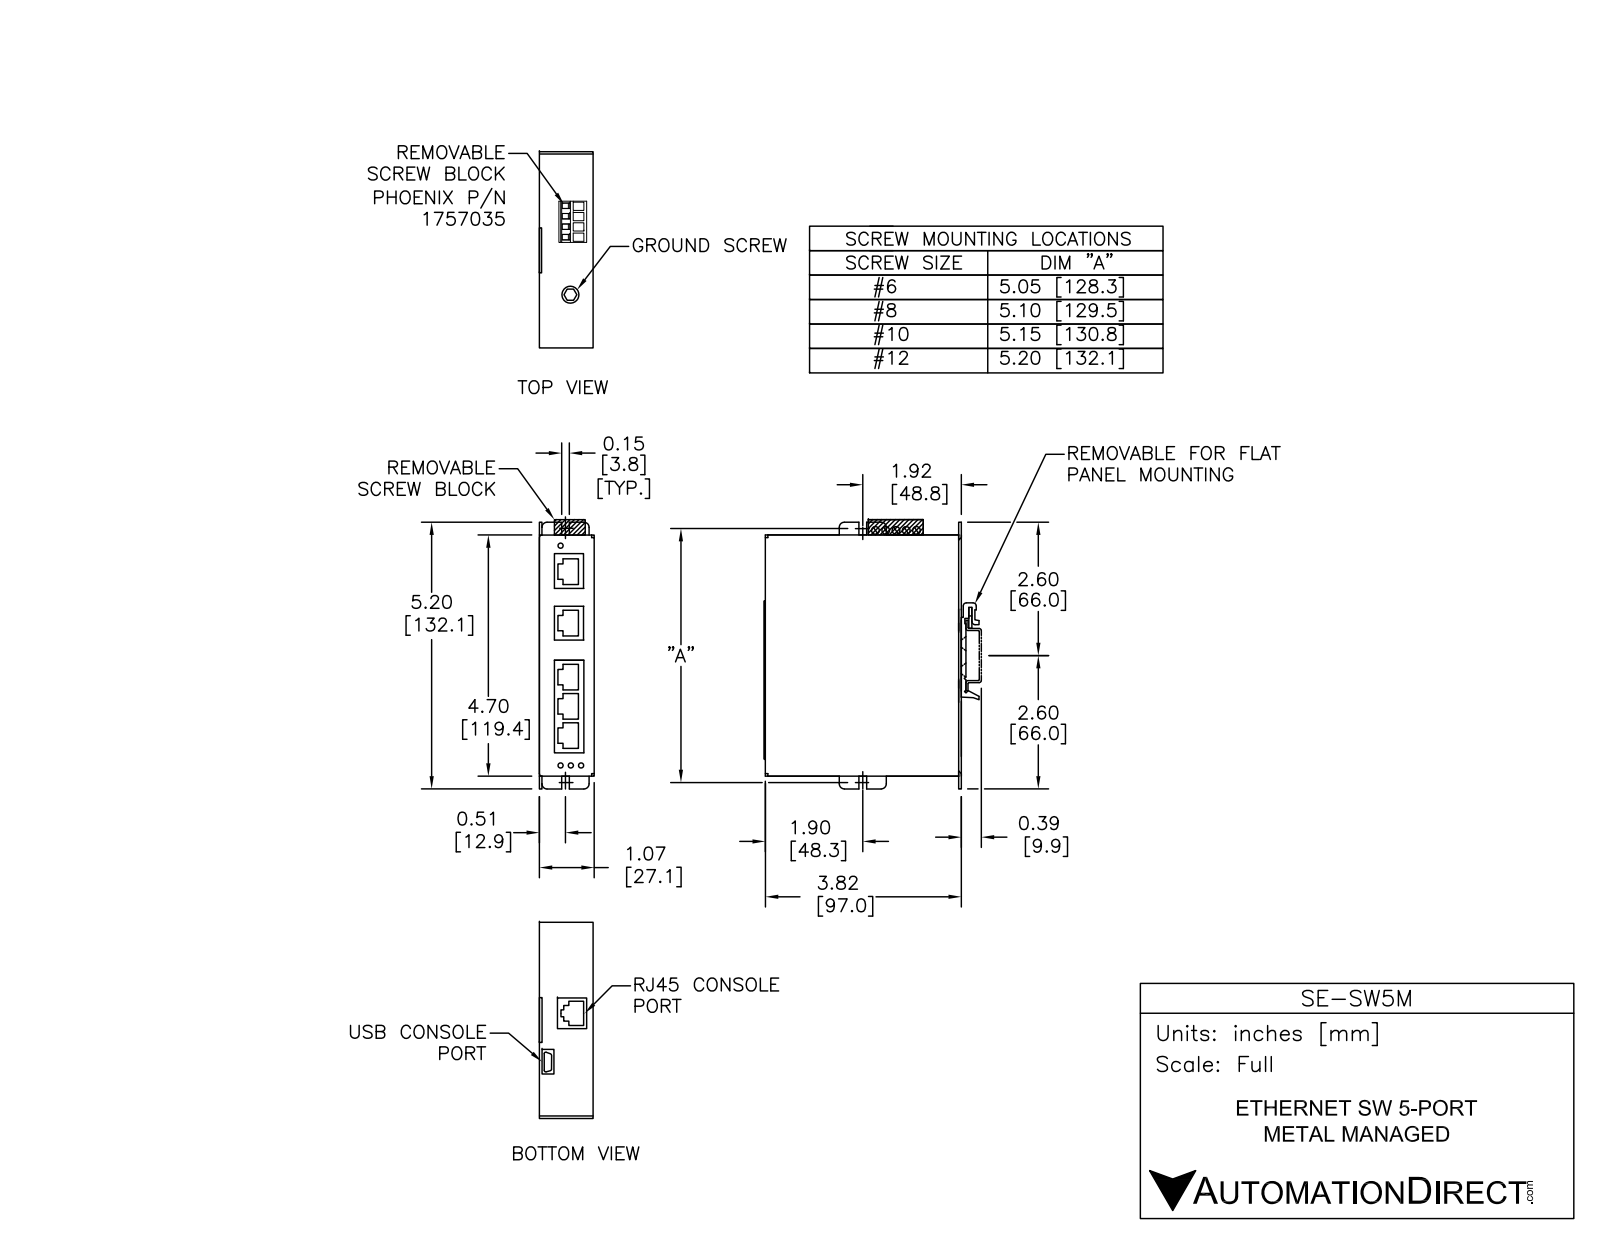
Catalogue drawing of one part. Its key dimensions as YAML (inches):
part_name: "SE-SW5M"
step_written_by: "SolidWorks 2011 (AUTOMOTIVE_DESIGN)"
units: inches
bodies: {solids: 1, faces: 344, planar: 302, cylindrical: 42, other: 0}
overall_size: [5.38, 4.231, 1.07]
volume: 19.27
surface_area: 103.7
round_holes:
  - {diameter: 0.11, count: 4}
  - {diameter: 0.15, count: 4}
  - {diameter: 0.215, count: 1}
round_bosses_or_shafts:
  - {diameter: 0.33, count: 1}
partial_cylinders:
  - {radius: 0.1, count: 8}
  - {radius: 0.03, count: 7}
  - {radius: 0.045, count: 4}
  - {radius: 0.07, count: 4}
  - {radius: 0.06, count: 3}
  - {radius: 0.075, count: 1}
  - {radius: 0.076, count: 1}
  - {radius: 0.125, count: 1}
face_to_face_distances: [0.054, 1.07, 0.055, 1.015, 1.016, 0.055, 4.7, 3.82, 3.766, 3.765]
hole_center_spacings: [0.185, 0.37, 0.164, 0.176, 0.341, 0.555, 4.372, 4.375]
